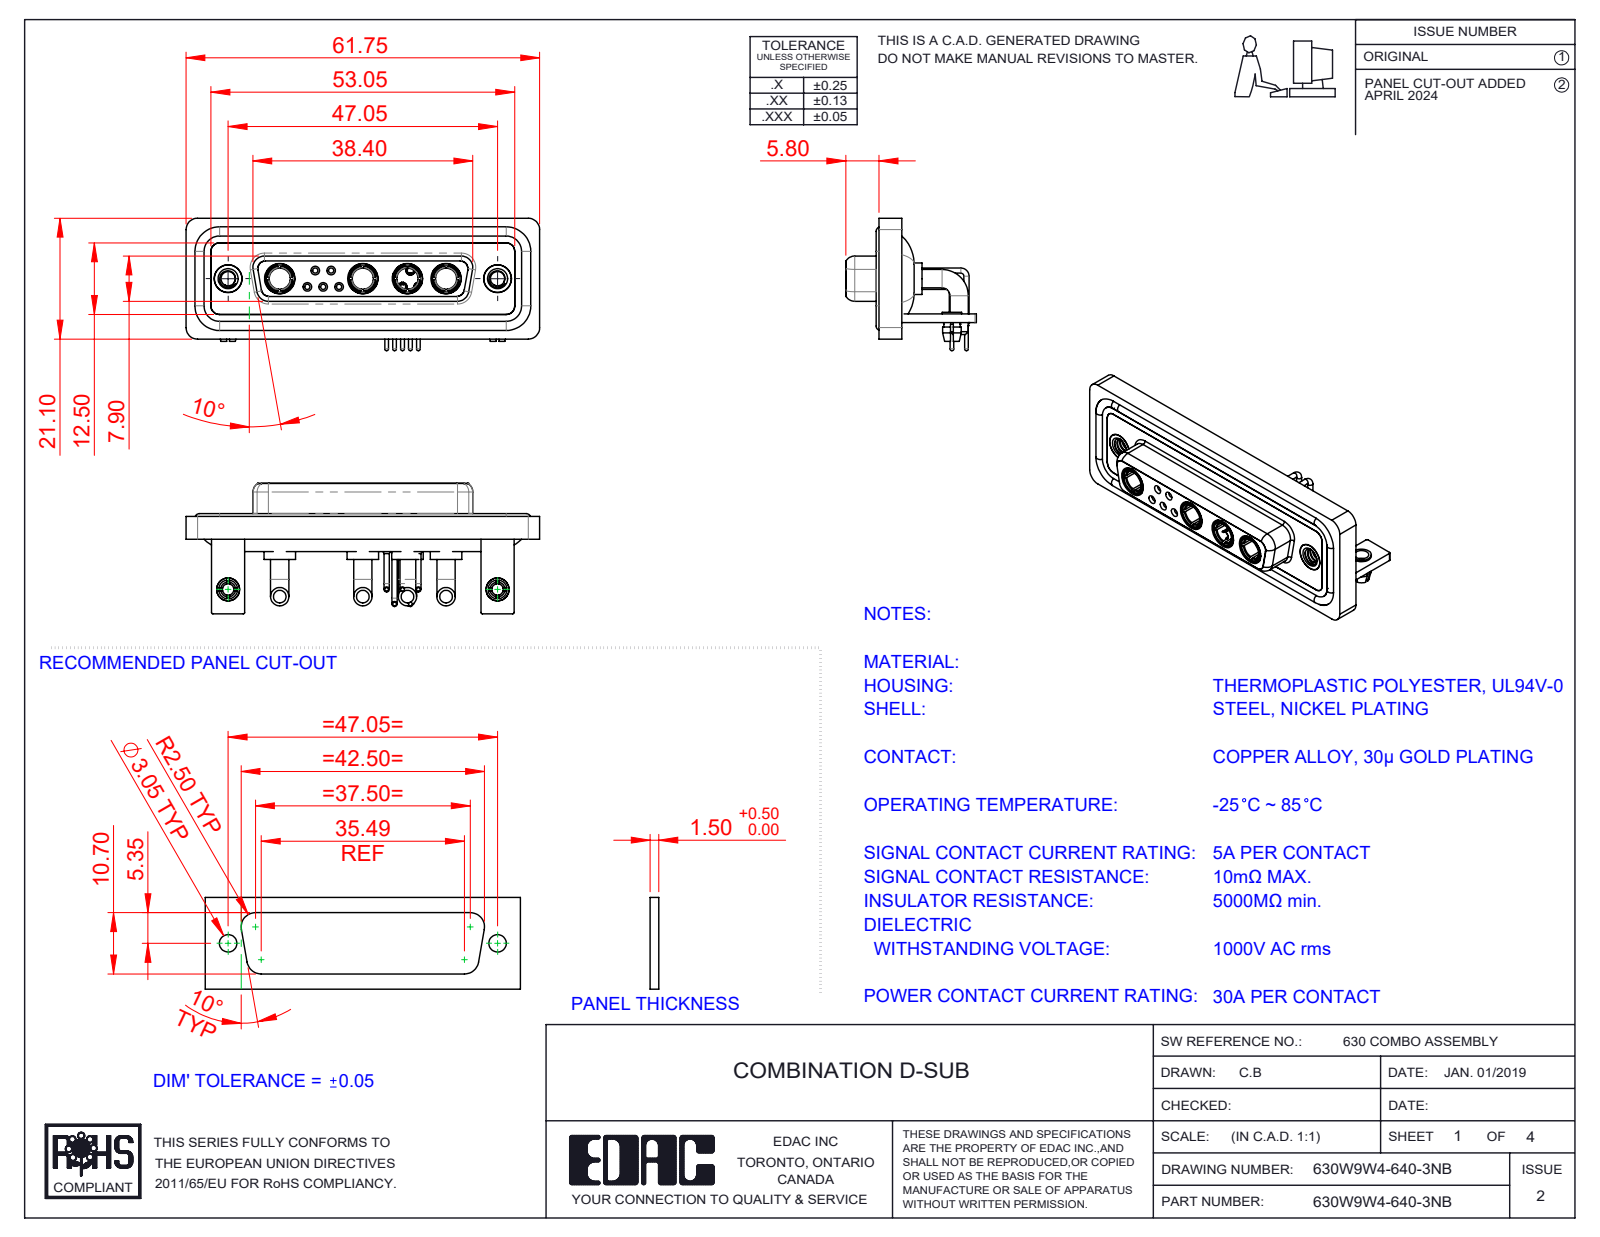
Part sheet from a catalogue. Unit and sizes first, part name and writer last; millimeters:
Units: millimetres
Overall size (bounding box): 61.75 × 23.12 × 22.8
Round holes (diameter × count): ⌀2 ×7, ⌀4.85 ×6, ⌀0.9 ×5, ⌀1.1 ×5, ⌀1.5 ×5, ⌀2.5 ×4, ⌀3.7 ×4, ⌀5.3 ×4, ⌀1.6 ×3, ⌀1.7 ×2, ⌀3.2 ×2, ⌀4 ×2
Round bosses / shafts (diameter × count): ⌀0.9 ×10, ⌀1.6 ×9, ⌀3.2 ×8, ⌀2 ×5, ⌀1.5 ×5, ⌀0.65 ×5, ⌀5.5 ×4, ⌀5.2 ×4
Partial cylindrical surfaces — rounded edges, fillets, slot ends (radius × count): R2 ×19, R1.5 ×18, R0.25 ×16, R1.35 ×8, R1.6 ×8, R0.5 ×5, R0.6 ×4, R0.65 ×4
Main face-to-face distances: 0.4, 1.8, 2.9, 3.7, 1.5, 4.1, 1.1, 1.4, 1.6, 2.5
Hole centre spacings: 3.16, 2.77, 5.04, 13.85, 11.08, 12.79, 15.5, 5.54
Volume: 8 959 mm³ · Surface area: 15 070 mm²
Bodies: 24 solids, 1097 faces (364 planar, 457 cylindrical, 276 other)
Part name (STEP PRODUCT): Power Socket_30A RA; 630Combo Shell Rear_25 Contacts; 630W9W4-640-3NB; 630Combo Waterproof Housing_25 Contacts (+7 more)
STEP written by: SolidWorks 2023 (CONFIG_CONTROL_DESIGN)
